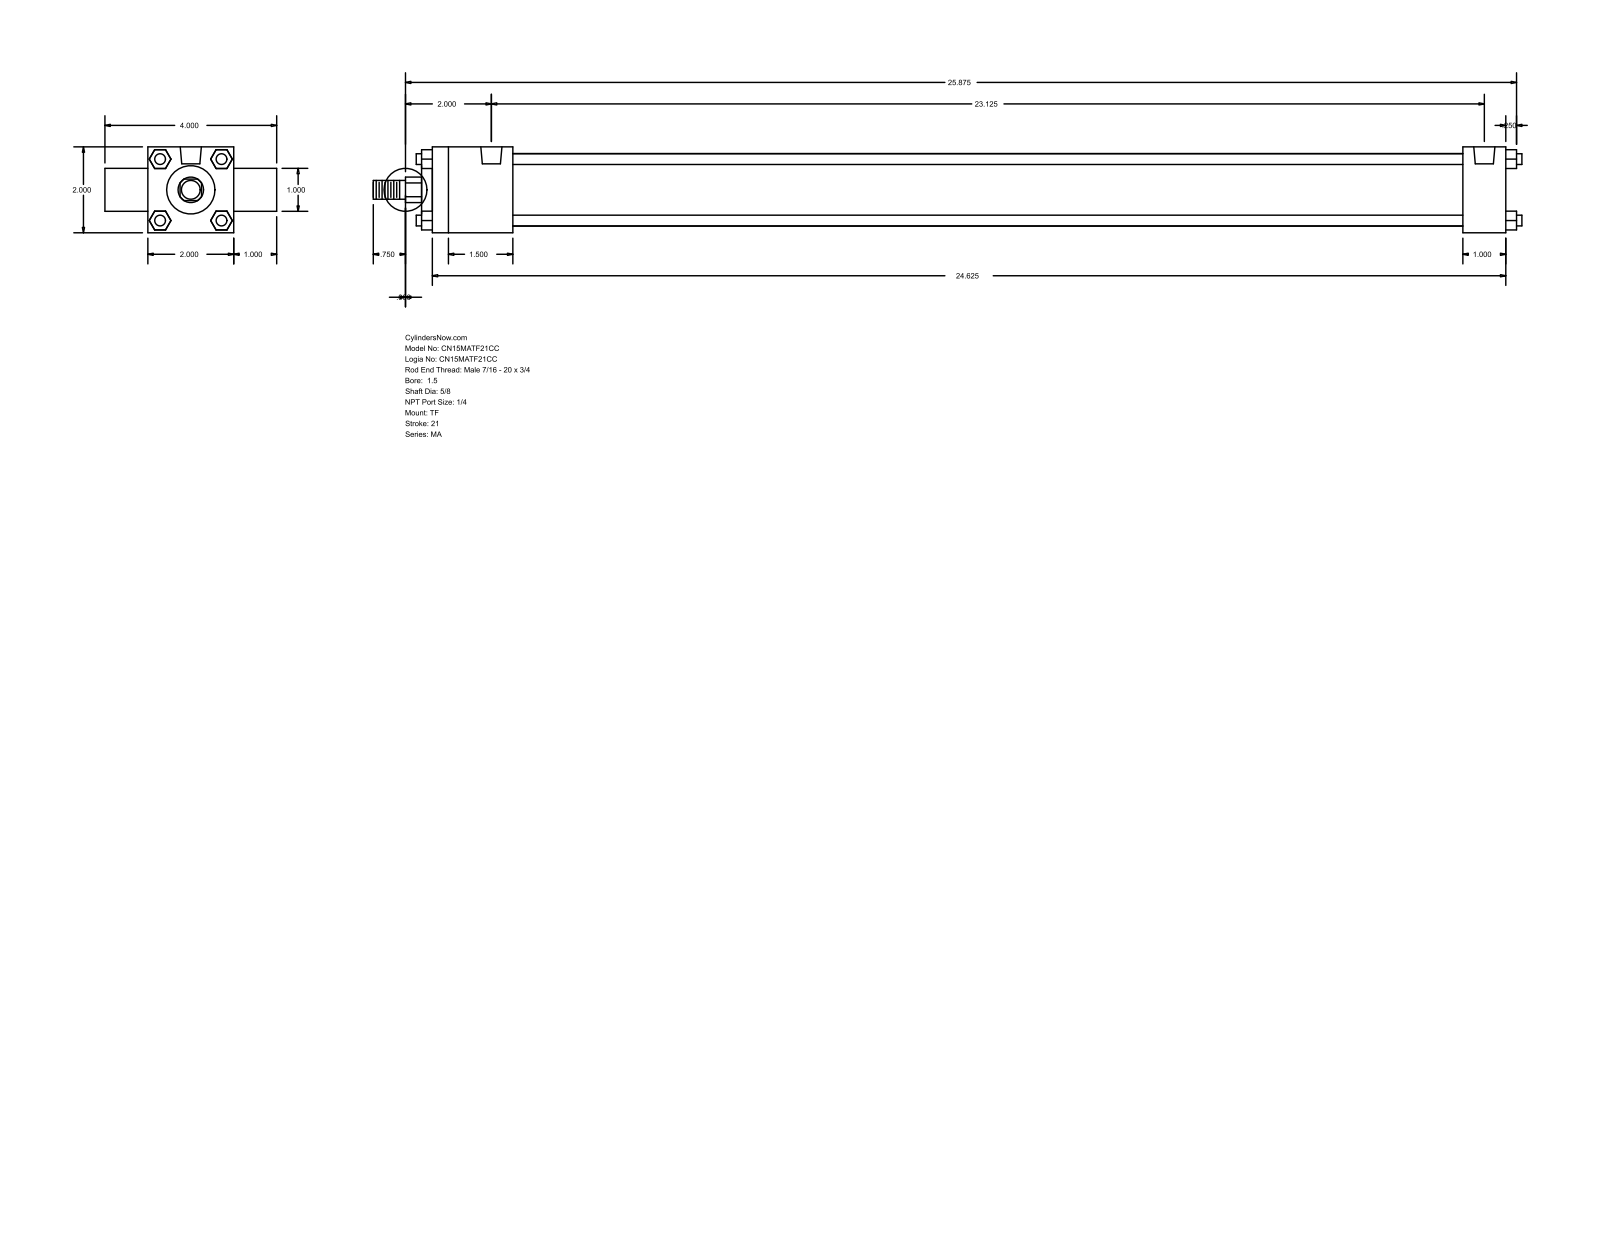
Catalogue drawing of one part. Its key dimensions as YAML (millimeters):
part_name: "MA_TF__0150_0.625"
step_written_by: "GSSL Pune (CONFIG_CONTROL_DESIGN)"
units: millimeters
bodies: {solids: 0, faces: 120, planar: 92, cylindrical: 28, other: 0}
overall_size: [679.45, 101.6, 50.8]
round_holes:
  - {diameter: 7.94, count: 3}
  - {diameter: 12.49, count: 2}
round_bosses_or_shafts:
  - {diameter: 6.35, count: 4}
  - {diameter: 42.93, count: 1}
  - {diameter: 28.57, count: 1}
  - {diameter: 25.4, count: 1}
  - {diameter: 15.88, count: 1}
  - {diameter: 11.11, count: 1}
partial_cylinders:
  - {radius: 7.54, count: 1}
face_to_face_distances: [50.8, 25.4, 635, 6.35, 641.35, 76.2, 47.62, 609.6, 561.98, 587.38]
hole_center_spacings: [587.37]
